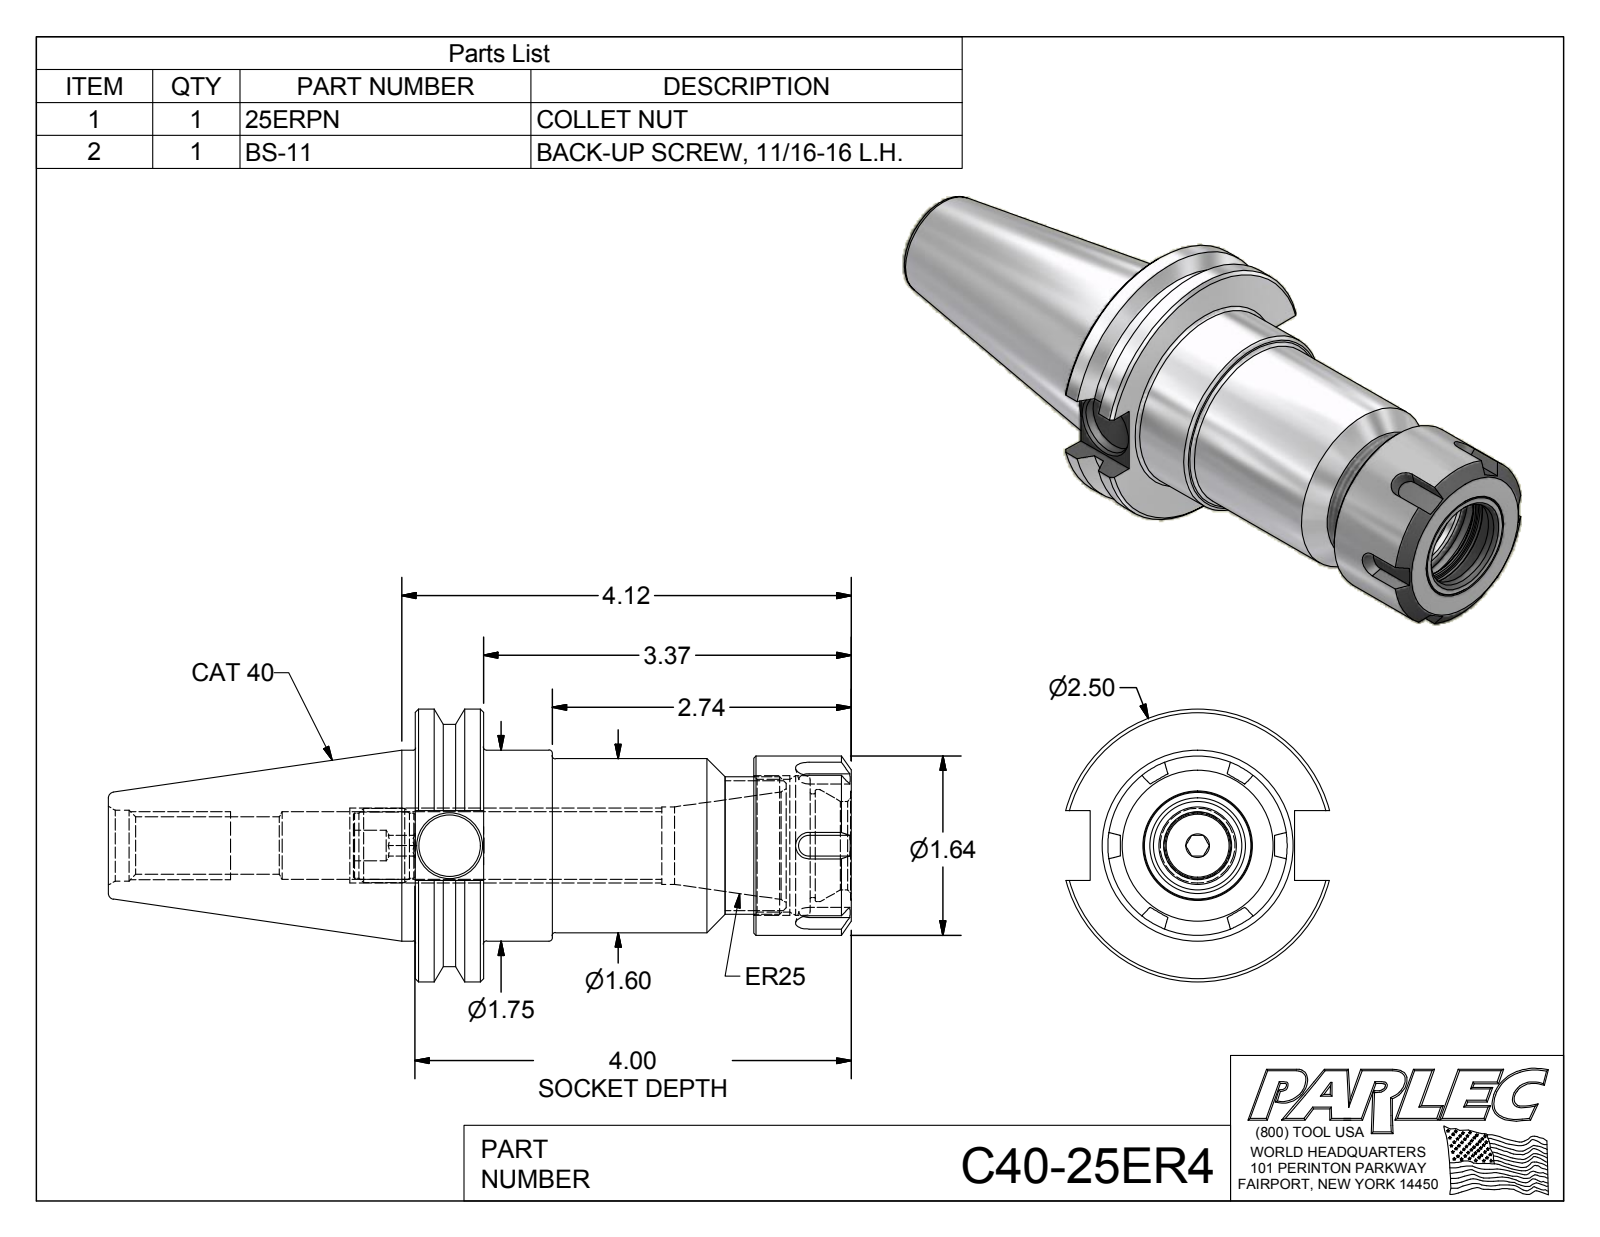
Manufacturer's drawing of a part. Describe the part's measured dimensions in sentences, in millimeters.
The part is named "C40-25ER4; C40-25ER4-1; 25ERPN; BS-11". Its 3-D file was written by "Autodesk Inventor 2012 (AUTOMOTIVE_DESIGN)". It is 3 solids with 117 faces: 43 planar, 25 cylindrical and 49 other. Overall it measures 172.9 by 63.5 by 61.4 millimeters. Its volume is 184 500 cubic millimeters and its surface area 40 710 square millimeters. Round holes: 1 of diameter 7.1, 1 of diameter 13.4, 1 of diameter 14.3, 1 of diameter 15.7, 1 of diameter 16.5, 1 of diameter 18, 1 of diameter 20.6, 1 of diameter 24.1, 1 of diameter 26.1, 1 of diameter 30.9, 1 of diameter 32.5. Round bosses or shafts: 1 of diameter 63.5, 1 of diameter 56.4, 1 of diameter 44.5, 1 of diameter 41.7, 1 of diameter 40.5, 1 of diameter 32, 1 of diameter 17.3, 1 of diameter 15.1. The main face-to-face distances are 15.9, 101.5, 85.6, 78.8, 62.9, 22.7, 91.9, 76.1, 13.2, 9.5.
